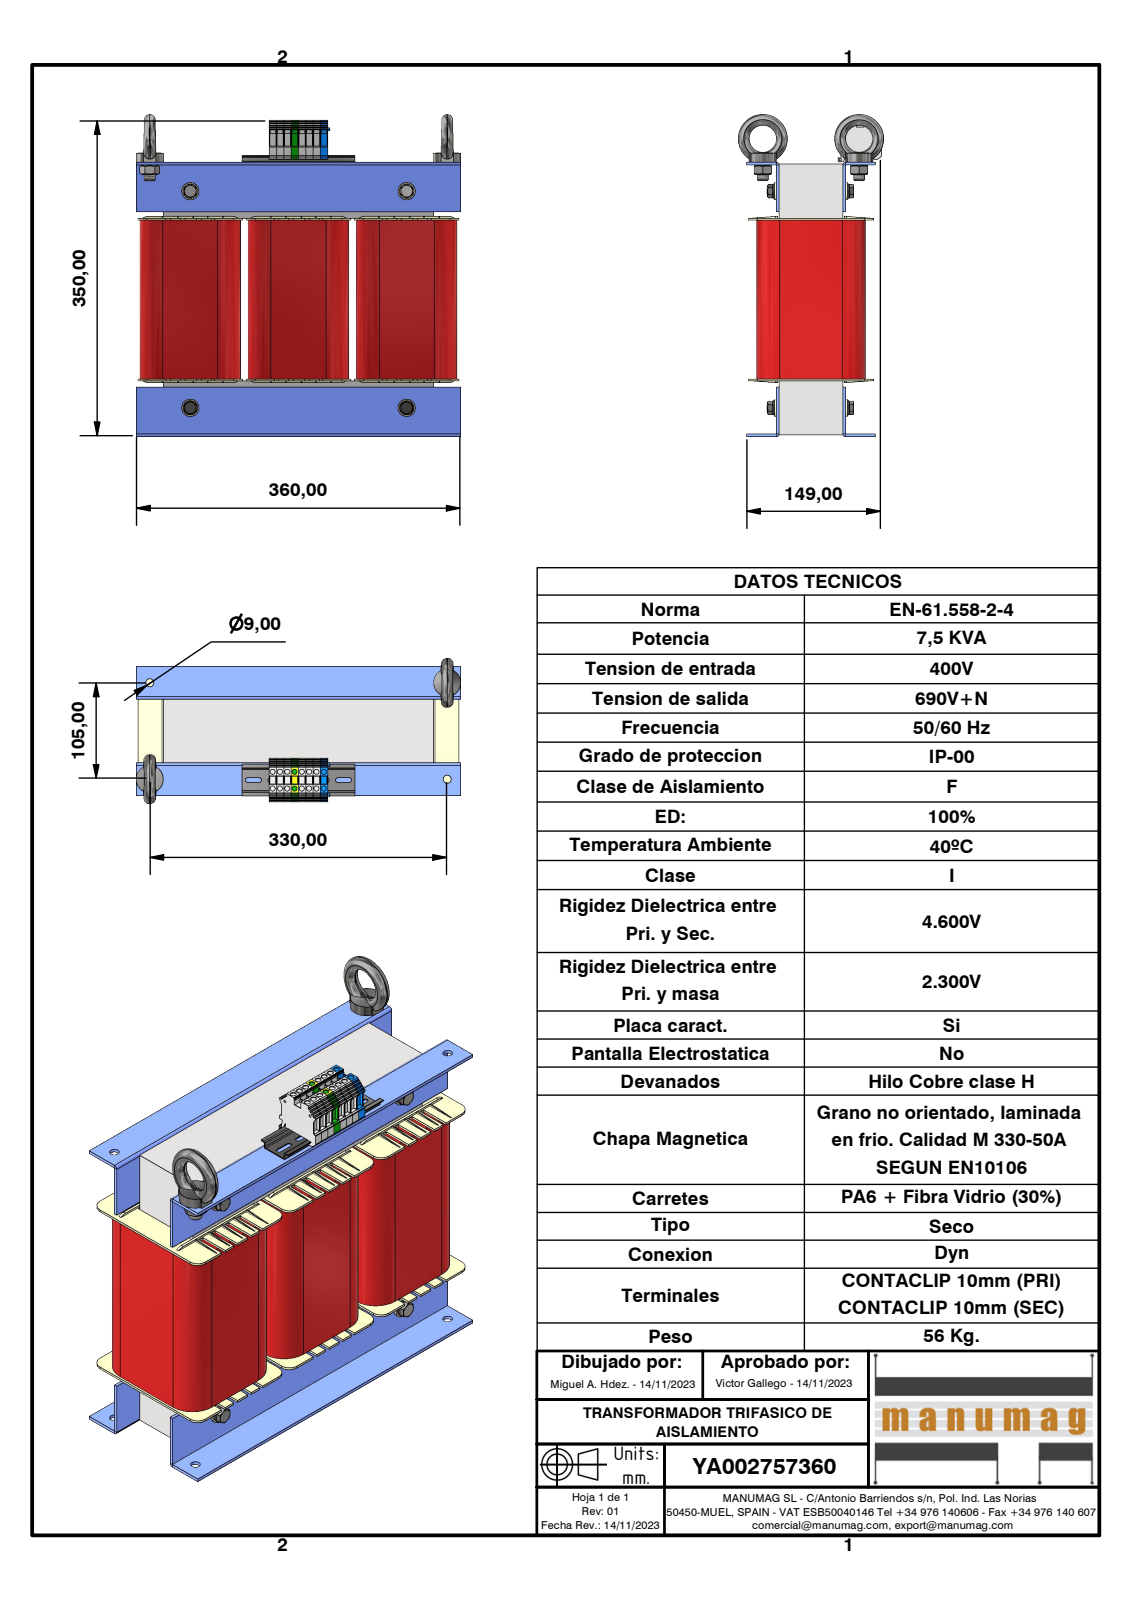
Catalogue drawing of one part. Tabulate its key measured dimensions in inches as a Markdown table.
| quantity | value |
| --- | --- |
| part name | YA002757360; UI 180 - 70 (300x300); UI 180_70_BOBINADO; RC60 NT060 (+8 more) |
| STEP written by | Autodesk Inventor 2023 (AUTOMOTIVE_DESIGN) |
| units | inches |
| bodies | 45 solids, 3384 faces (2398 planar, 798 cylindrical, 188 other) |
| overall size | 14.173 × 14.055 × 6.299 |
| volume | 590.3 in³ |
| surface area | 2 220 in² |
| round holes (diameter × count) | 0.224 × 16, 0.262 × 4, 0.315 × 4, 0.331 × 4, 0.354 × 4, 0.413 × 4, 0.433 × 4, 0.094 × 2, 0.098 × 2, 0.108 × 2, 0.398 × 2, 1.181 × 2 |
| round bosses / shafts (diameter × count) | 0.748 × 4, 0.63 × 4, 0.449 × 4, 0.378 × 4, 0.288 × 4, 2.126 × 2, 0.472 × 2, 0.425 × 2 |
| partial cylindrical surfaces (radius × count) | 0.012 × 81, 0.039 × 28, 0.394 × 24, 0.079 × 17, 0.118 × 12, 0.13 × 12, 0.999 × 12, 0.102 × 10 |
| main face-to-face distances | 0.098, 0.039, 9.449, 0.059, 0.118, 2.874, 2.362, 2.756, 4.724, 0.869 |
| hole center spacings | 0.319, 0.791, 0.638, 0.965, 0.957, 1.2, 0.724, 1.276 |
